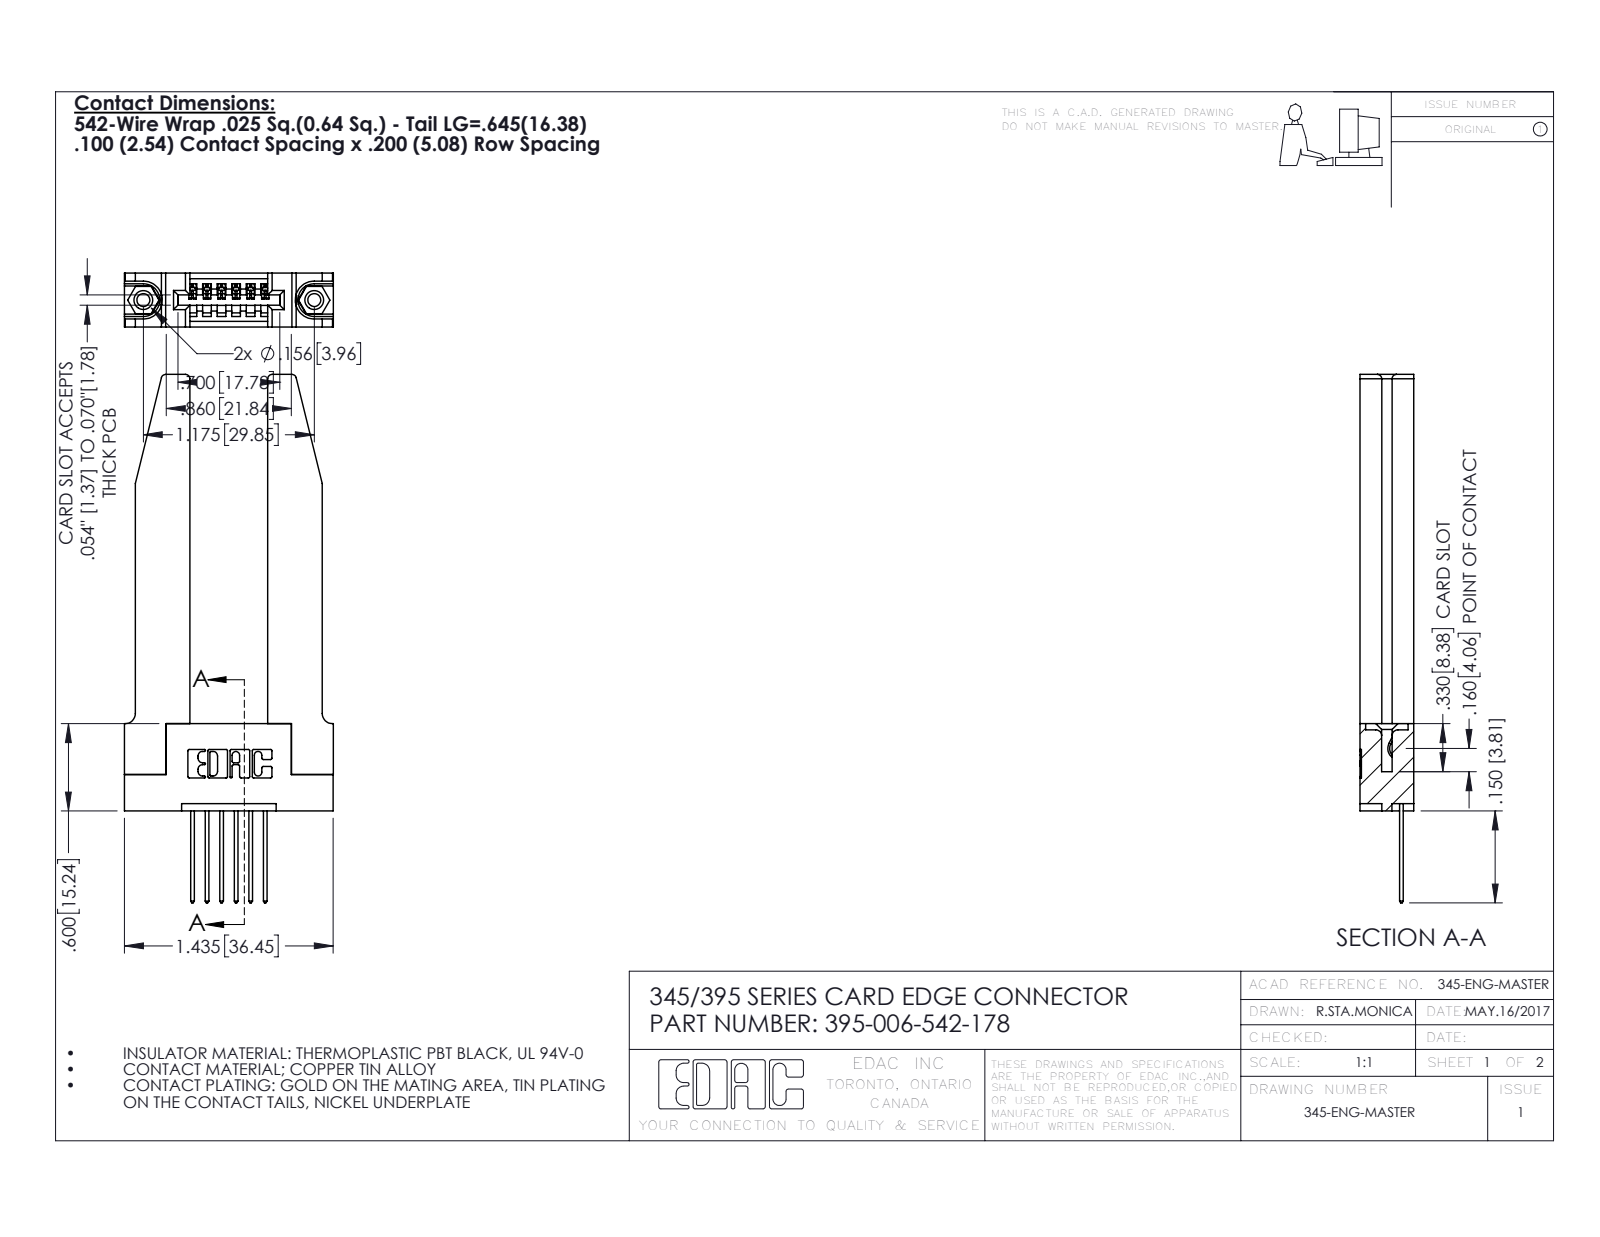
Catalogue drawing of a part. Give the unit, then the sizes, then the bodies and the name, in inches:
Units: inches
Overall size (bounding box): 3.632 × 1.436 × 0.37
Round holes (diameter × count): ⌀0.089 ×2, ⌀0.125 ×2, ⌀0.156 ×2, ⌀0.064 ×1
Round bosses / shafts (diameter × count): ⌀0.155 ×2
Partial cylindrical surfaces — rounded edges, fillets, slot ends (radius × count): R0.01 ×22, R0.006 ×12, R0.01 ×12, R0.03 ×8, R0.007 ×6, R0.031 ×6, R0.026 ×3, R0.031 ×2
Main face-to-face distances: 0.37, 0.15, 0.22, 0.072, 0.535, 0.148, 0.298, 0.077, 0.2, 0.095
Hole centre spacings: 0.27, 0.946, 1.175
Volume: 0.668 in³ · Surface area: 16.54 in²
Bodies: 11 solids, 708 faces (462 planar, 194 cylindrical, 52 other)
Part name (STEP PRODUCT): 345-220-078_345-220-078; 345-250-001_345-250-001-102; 395-006-542-178; 345-292-001_345-293-142 (+1 more)
STEP written by: SolidWorks 2016 (CONFIG_CONTROL_DESIGN)
